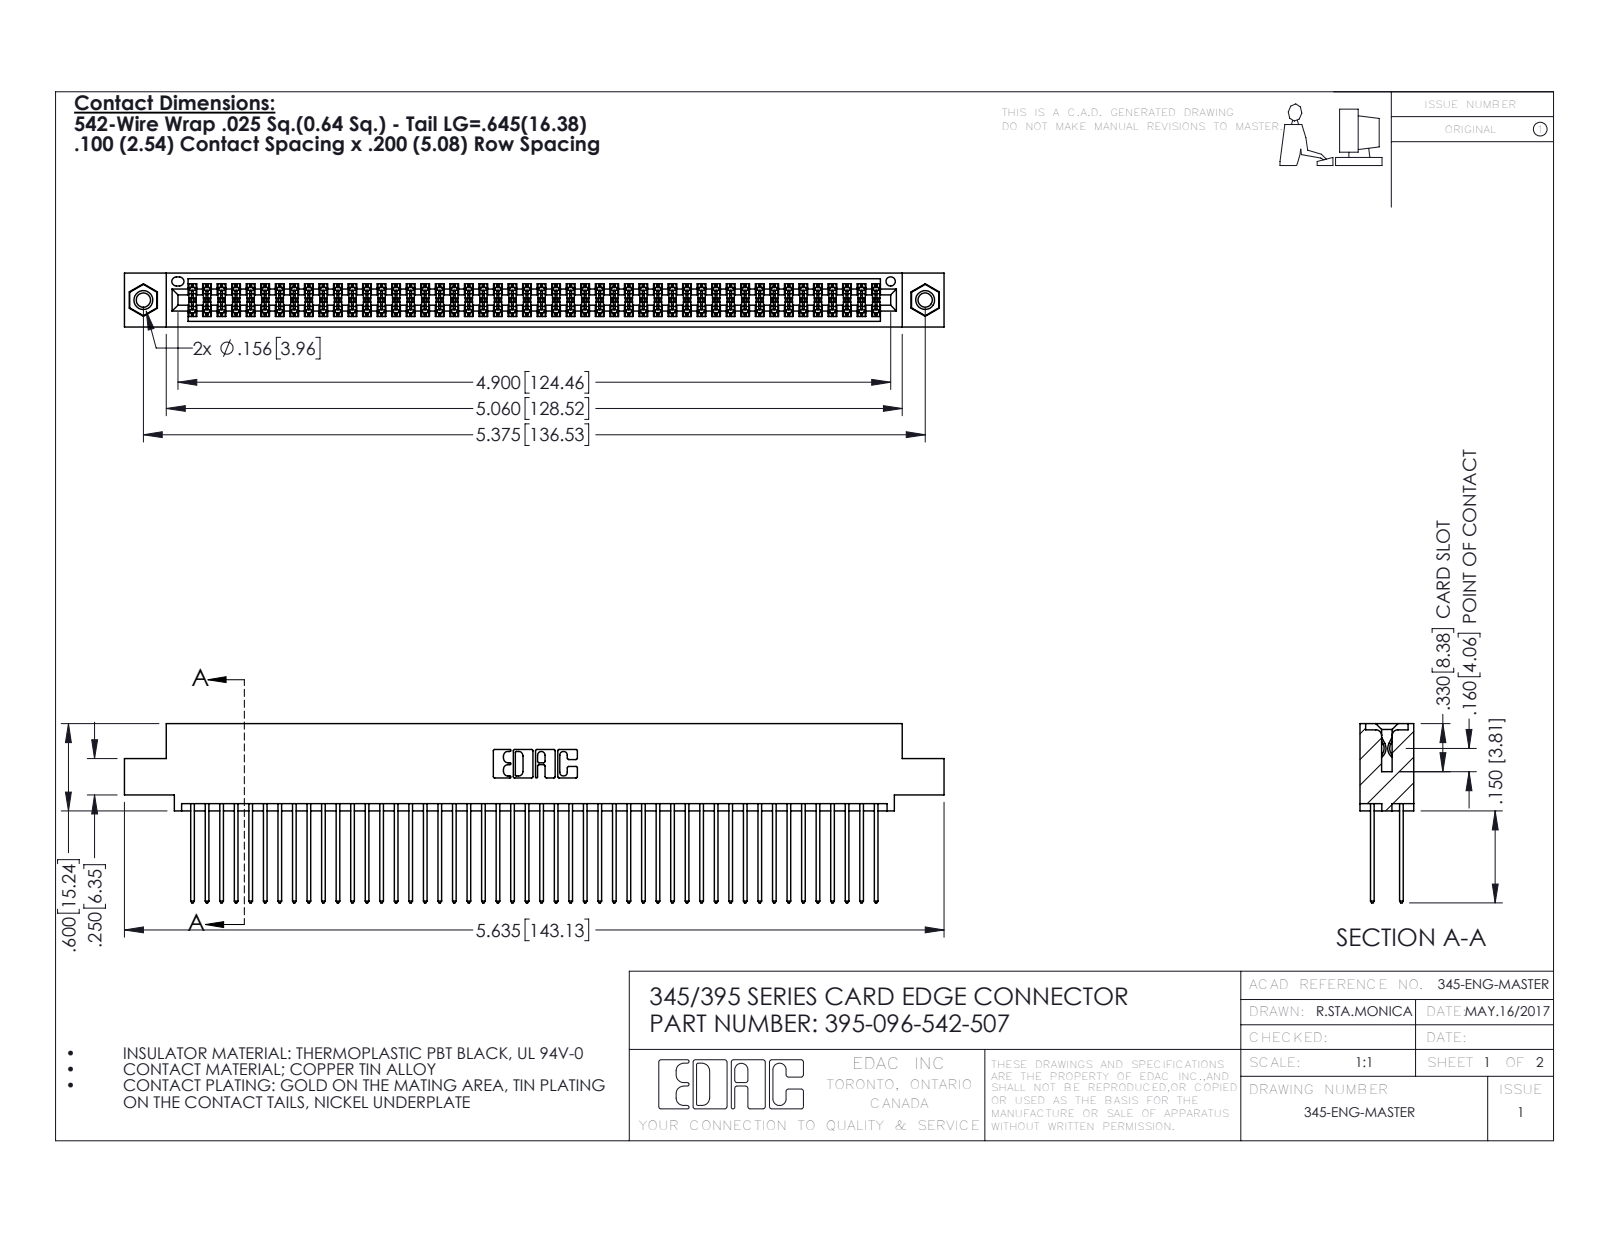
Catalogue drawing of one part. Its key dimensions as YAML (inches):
part_name: "345-292-001_345-293-142; 345 Part_0.110 Offset - 0.156 Dia-TI; 345-250-001_345-250-005-103; 395-096-542-507"
step_written_by: "SolidWorks 2016 (CONFIG_CONTROL_DESIGN)"
units: inches
bodies: {solids: 99, faces: 4990, planar: 3284, cylindrical: 1690, other: 16}
overall_size: [5.635, 1.232, 0.37]
volume: 0.874
surface_area: 36.42
round_holes:
  - {diameter: 0.098, count: 2}
  - {diameter: 0.125, count: 2}
  - {diameter: 0.156, count: 2}
  - {diameter: 0.064, count: 1}
round_bosses_or_shafts:
  - {diameter: 0.155, count: 2}
partial_cylinders:
  - {radius: 0.006, count: 144}
  - {radius: 0.01, count: 96}
  - {radius: 0.01, count: 22}
  - {radius: 0.007, count: 6}
  - {radius: 0.031, count: 6}
  - {radius: 0.026, count: 3}
  - {radius: 0.014, count: 2}
  - {radius: 0.019, count: 2}
face_to_face_distances: [0.072, 0.298, 0.2, 0.098, 0.272, 0.025, 0.225, 0.37, 0.175, 0.149]
hole_center_spacings: [0.27, 5.139, 5.375]
